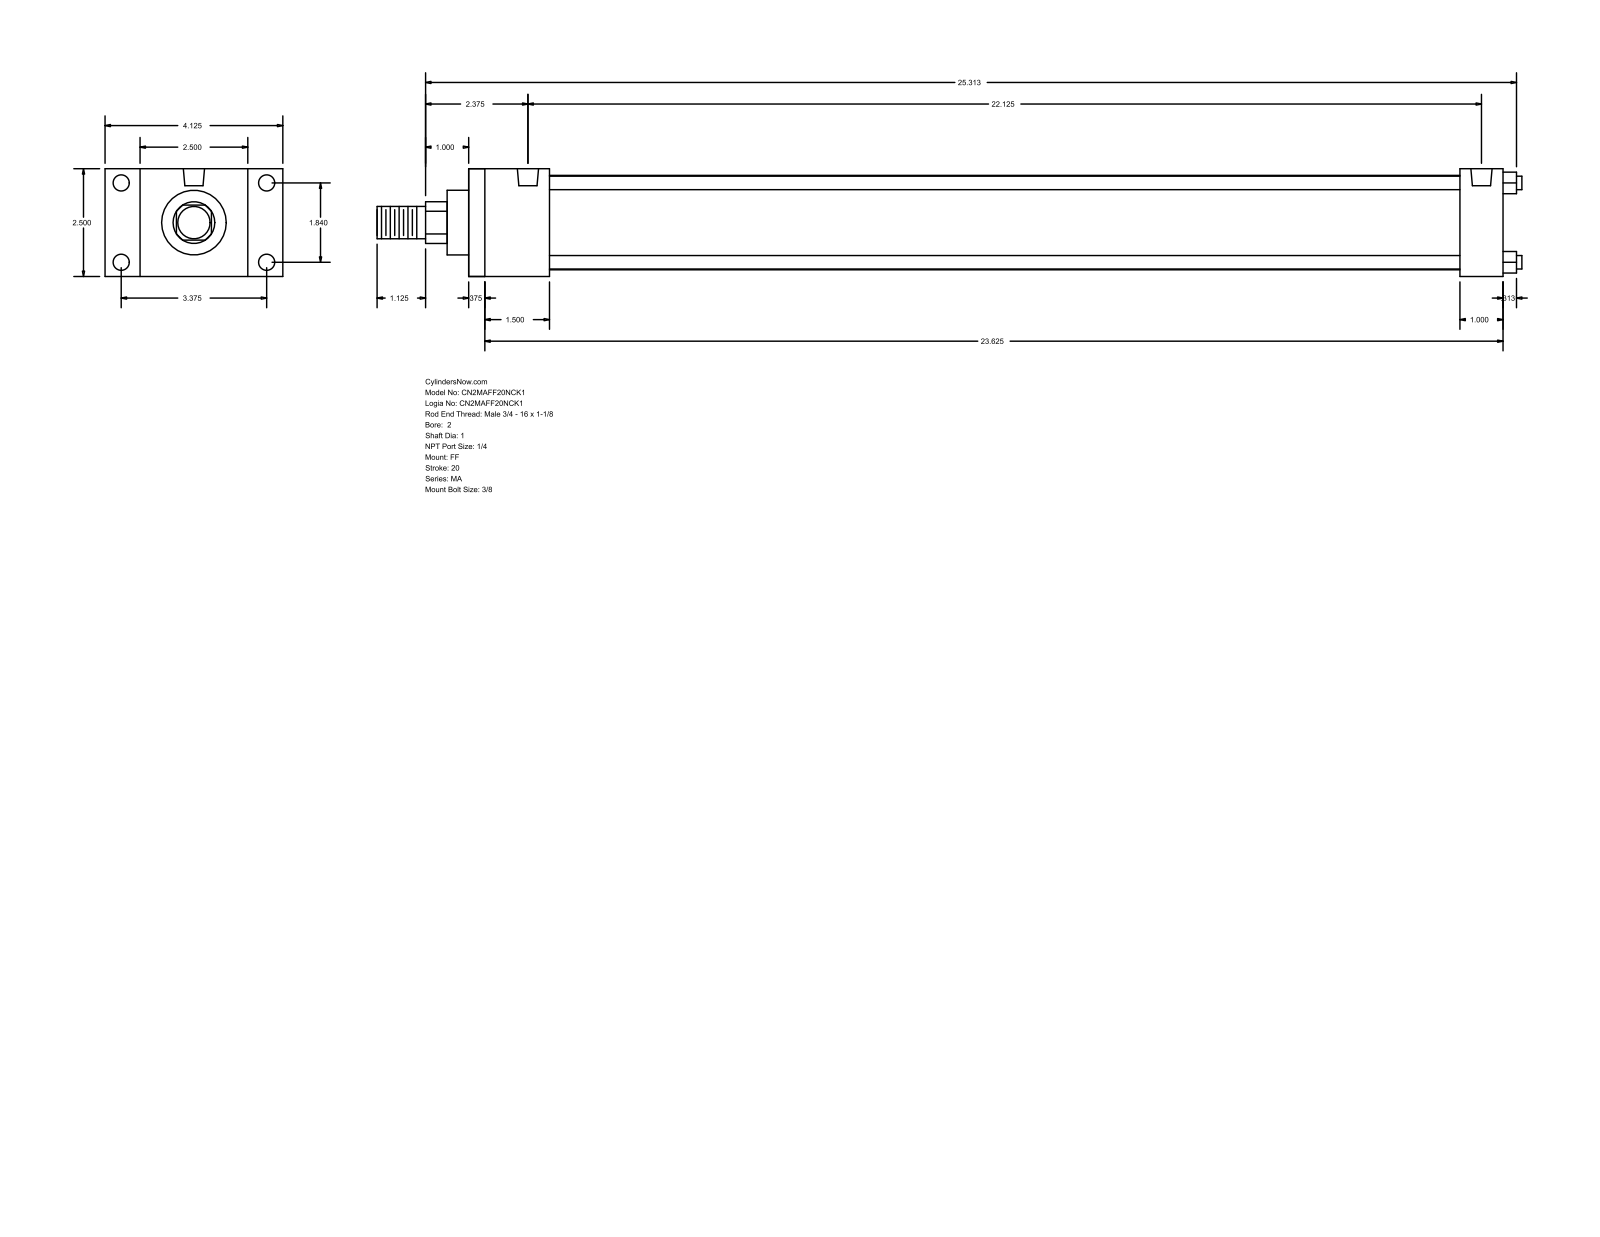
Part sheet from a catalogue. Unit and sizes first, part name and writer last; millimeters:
Units: millimetres
Overall size (bounding box): 674.69 × 104.78 × 63.5
Round holes (diameter × count): ⌀7.94 ×4, ⌀9.53 ×4, ⌀12.49 ×2
Round bosses / shafts (diameter × count): ⌀7.94 ×4, ⌀55.63 ×1, ⌀38.1 ×1, ⌀25.4 ×1, ⌀19.05 ×1
Partial cylindrical surfaces — rounded edges, fillets, slot ends (radius × count): R12.29 ×1
Main face-to-face distances: 63.5, 609.6, 9.52, 600.08, 25.4, 20.64, 12.7, 47.63, 584.2, 38.11
Hole centre spacings: 46.74, 85.72, 97.63, 561.97
Bodies: 0 solids, 92 faces (64 planar, 28 cylindrical, 0 other)
Part name (STEP PRODUCT): MA_FF__0200_1
STEP written by: GSSL Pune (CONFIG_CONTROL_DESIGN)
